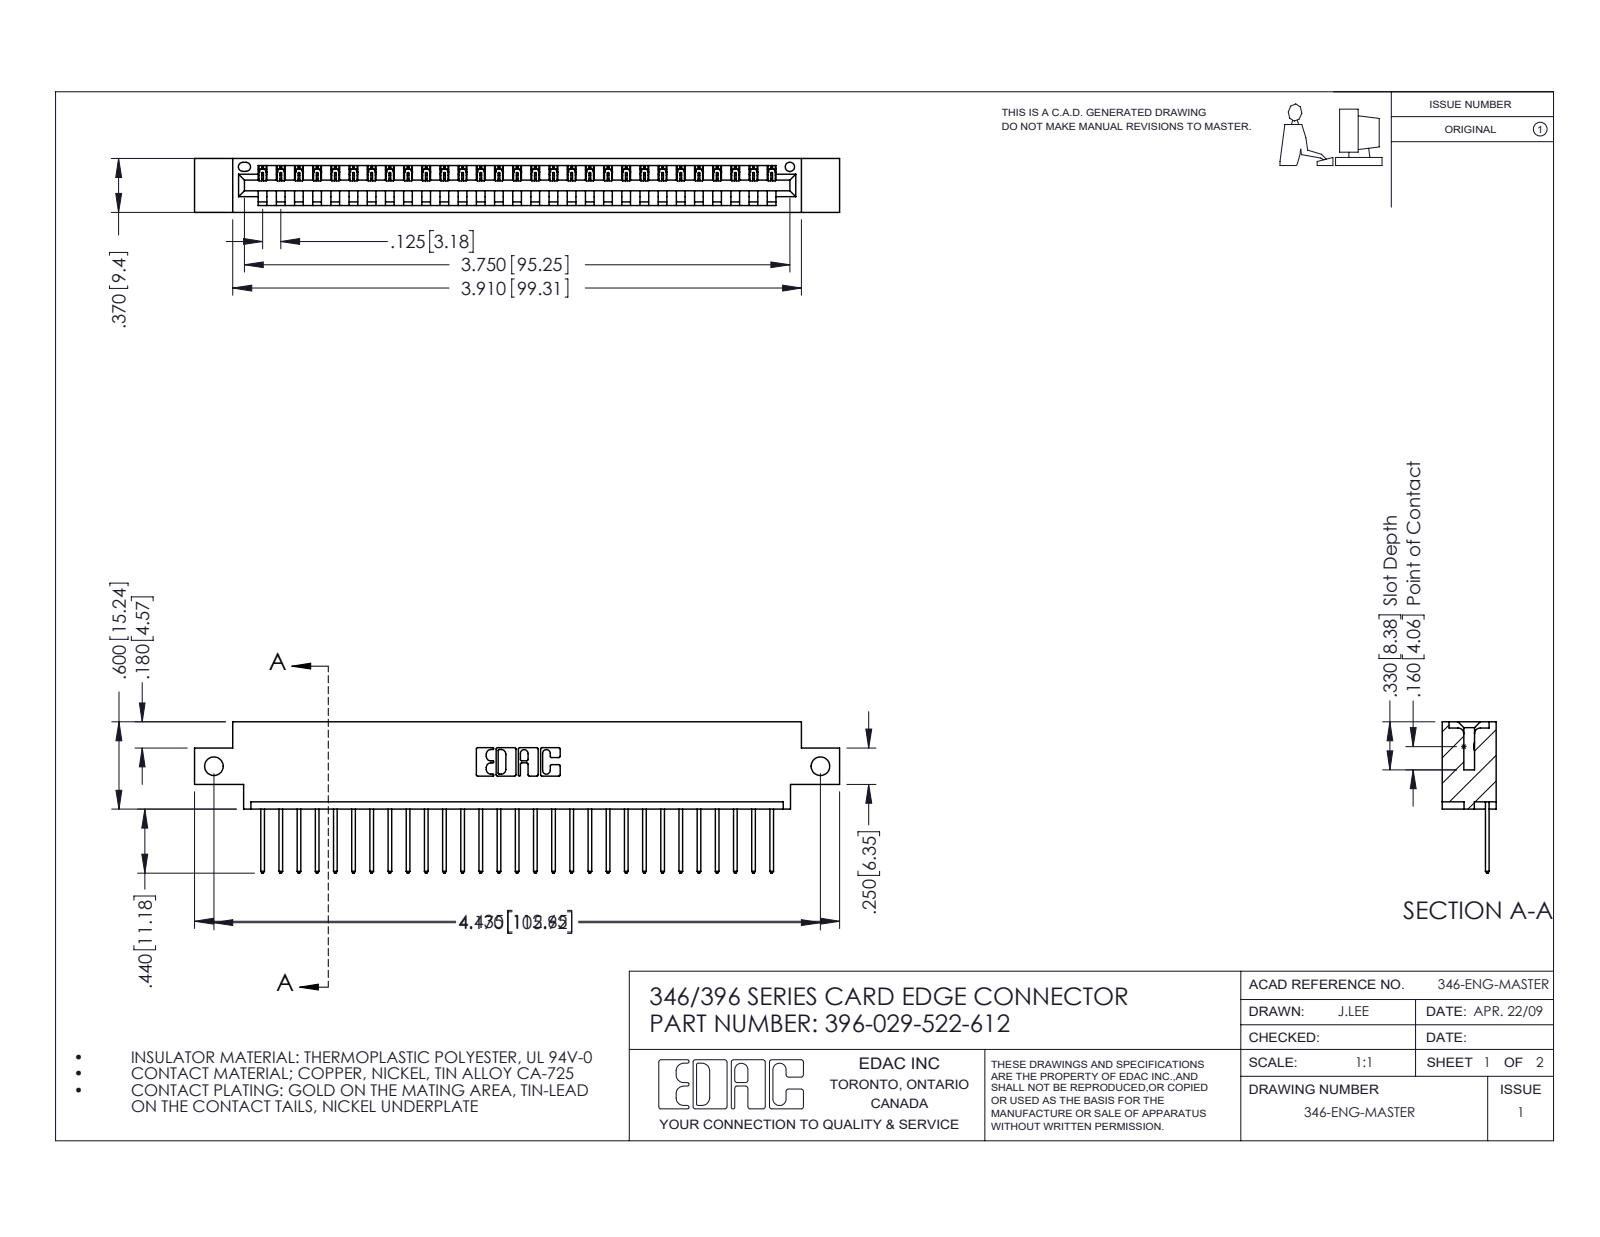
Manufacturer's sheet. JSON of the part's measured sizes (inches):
{"part_name": "345-292-001_345-293-122; 346 Part_0.170 Offset - Side Mount; 396-029-522-612", "step_written_by": "SolidWorks 2016 (CONFIG_CONTROL_DESIGN)", "units": "inches", "bodies": {"solids": 30, "faces": 1808, "planar": 1240, "cylindrical": 568, "other": 0}, "overall_size": [4.435, 1.04, 0.37], "volume_in3": 0.638, "surface_area_in2": 20.23, "round_holes": [[0.128, 2], [0.064, 1]], "partial_cylinders_radius": [[0.006, 58], [0.01, 58], [0.01, 22], [0.007, 6], [0.031, 6], [0.026, 3], [0.031, 2], [0.04, 2]], "face_to_face_distances": [0.048, 0.322, 0.37, 0.25, 0.072, 0.298, 0.025, 0.148, 0.222, 0.1], "hole_center_spacings": [4.17]}
